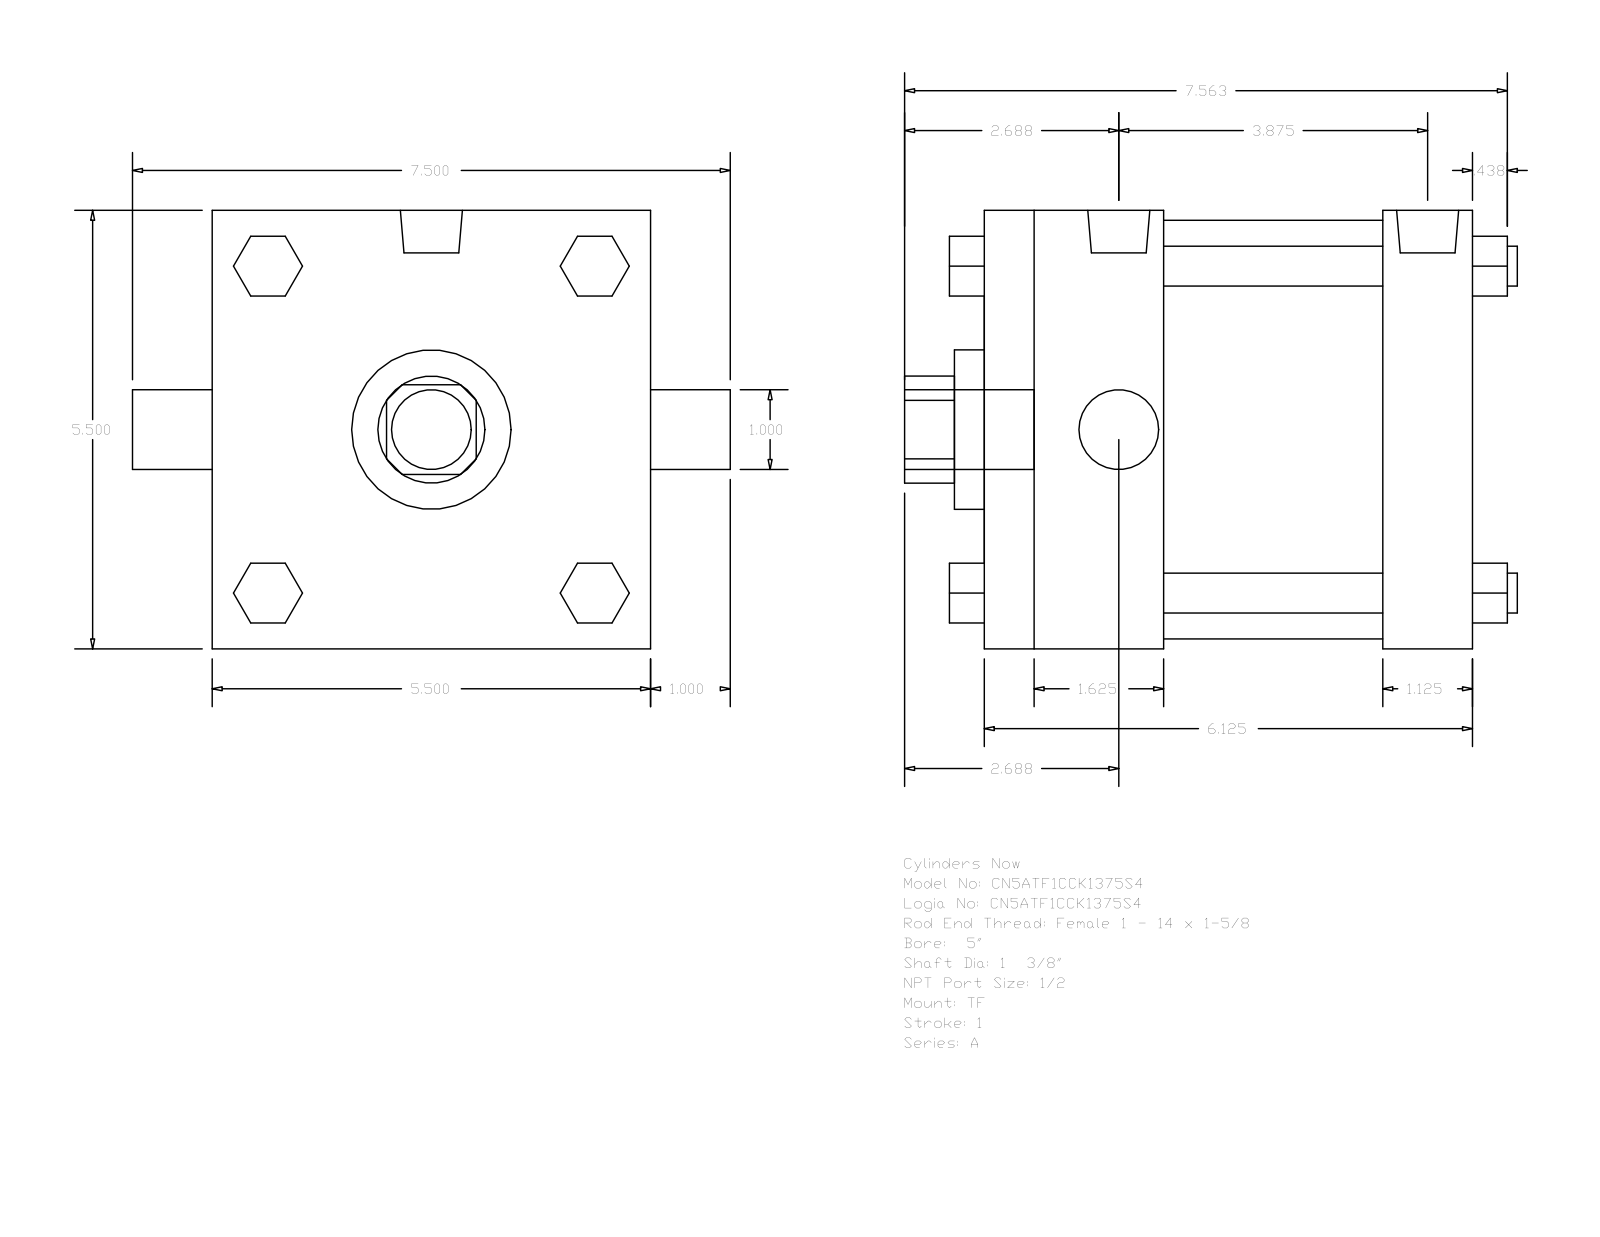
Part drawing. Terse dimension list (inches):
name: A_TF__0500_1.375
written by: GSSL Pune (CONFIG_CONTROL_DESIGN)
unit: in
bodies: 0 solids, 120 faces (92 planar, 28 cylindrical, 0 other)
size: 7.687 × 7.5 × 5.5
holes: 1× ⌀1, 1× ⌀1.375, 1× ⌀2, 1× ⌀5.25
bosses: 4× ⌀0.5, 3× ⌀0.344, 2× ⌀0.778, 1× ⌀1
rounds: 1× R0.672
face distances: 5.5, 6.125, 1.125, 2.75, 5, 2.25, 3.875, 0.75, 2.05, 3.55
